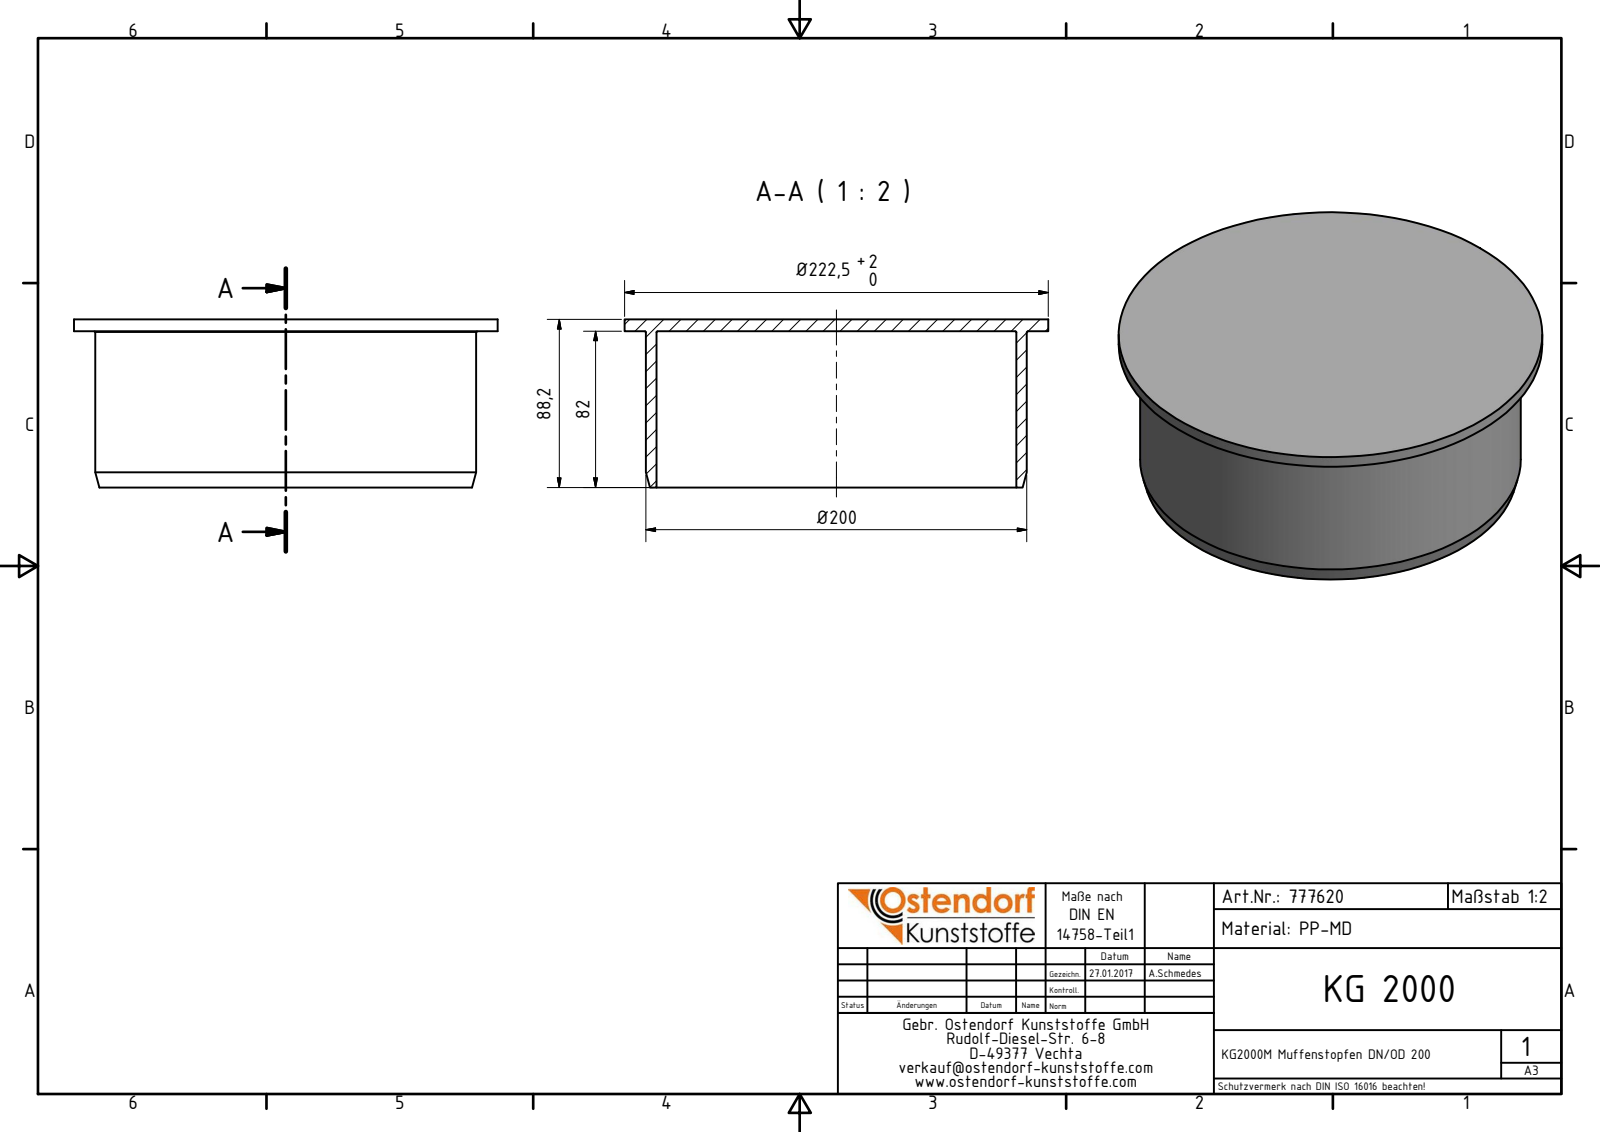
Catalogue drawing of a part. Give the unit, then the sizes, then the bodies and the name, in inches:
Units: inches
Overall size (bounding box): 8.76 × 8.76 × 3.472
Round holes (diameter × count): ⌀7.441 ×1
Round bosses / shafts (diameter × count): ⌀8.76 ×1, ⌀7.874 ×1
Main face-to-face distances: 0.244, 3.228, 3.472
Volume: 31.21 in³ · Surface area: 280.3 in²
Bodies: 1 solid, 10 faces (4 planar, 3 cylindrical, 3 other)
Part name (STEP PRODUCT): 777620 KG2000M Muffenstopfen DN_OD 200
STEP written by: Autodesk Inventor 2016 (AUTOMOTIVE_DESIGN)
